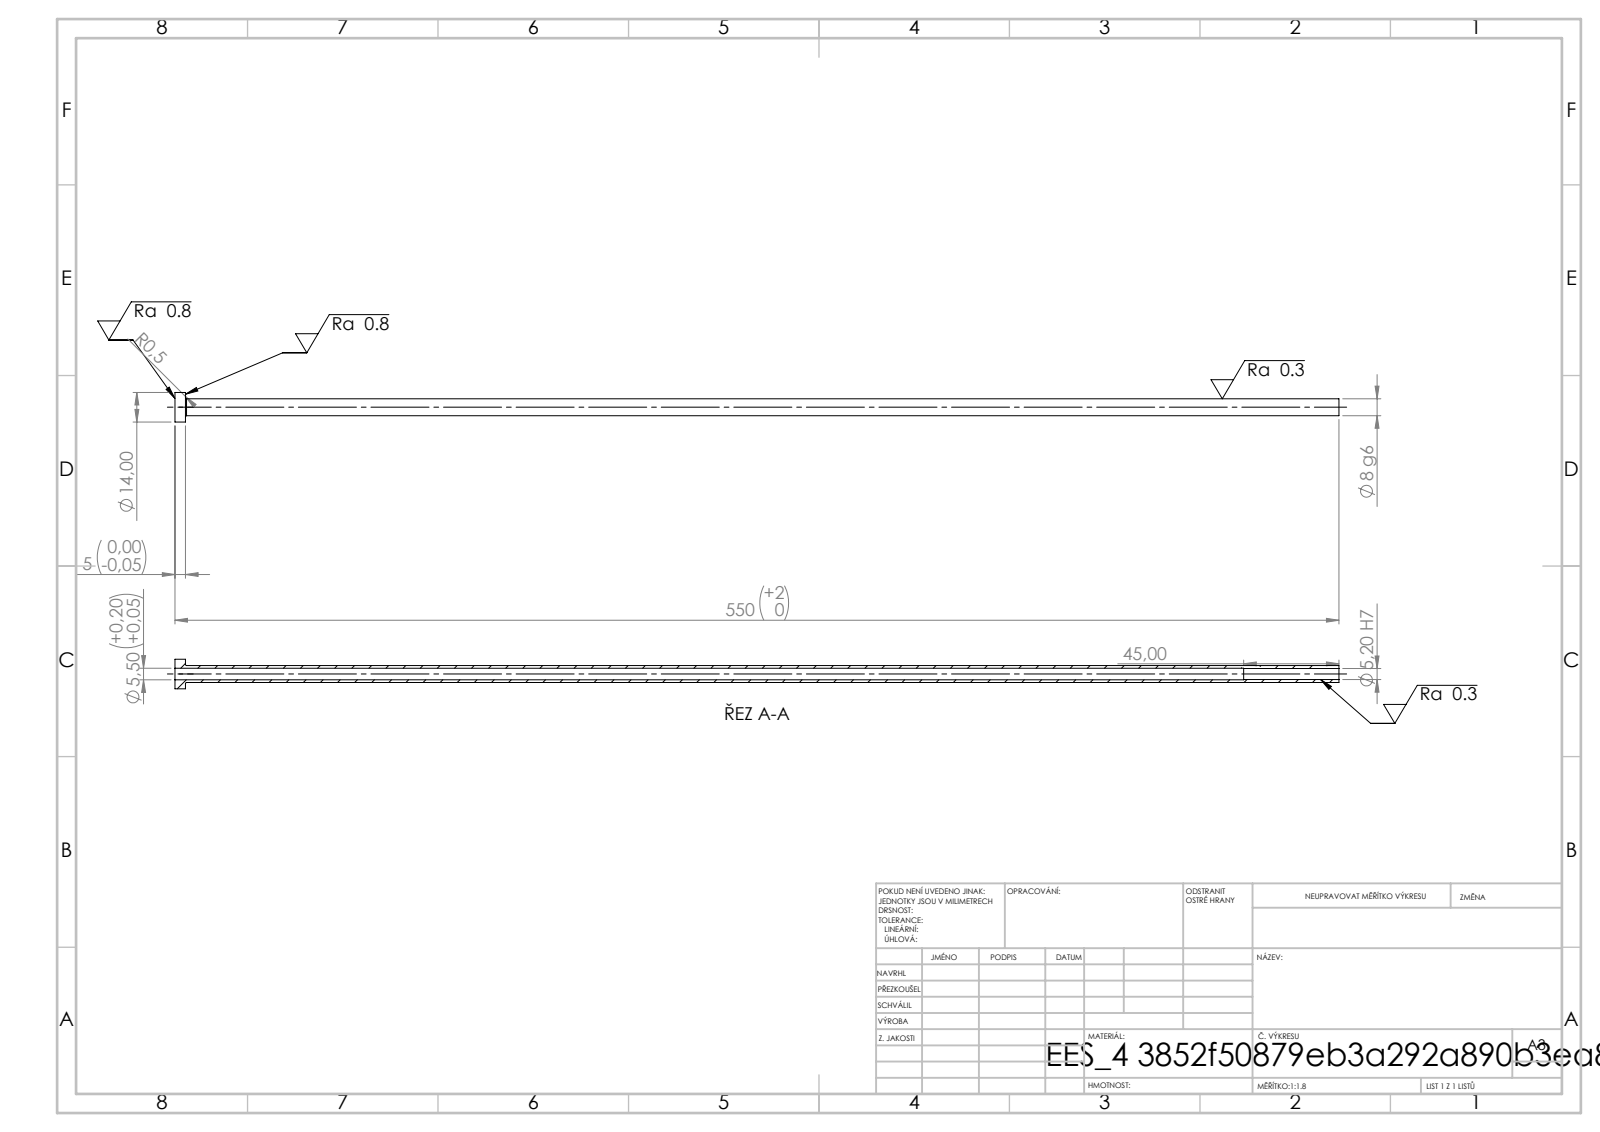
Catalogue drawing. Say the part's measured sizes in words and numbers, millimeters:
Its 3-D file was written by "SolidWorks 2019 (CONFIG_CONTROL_DESIGN)". It is 1 solid with 14 faces: 4 planar, 8 cylindrical and 2 other. Overall it measures 550 by 14 by 14 millimeters. Its volume is 15 212 cubic millimeters and its surface area 23 638 square millimeters. Round holes: 1 of diameter 5.2, 1 of diameter 5.5. Round bosses or shafts: 1 of diameter 14, 1 of diameter 8. The main face-to-face distances are 5, 550, 545, 505, 500, 45.
